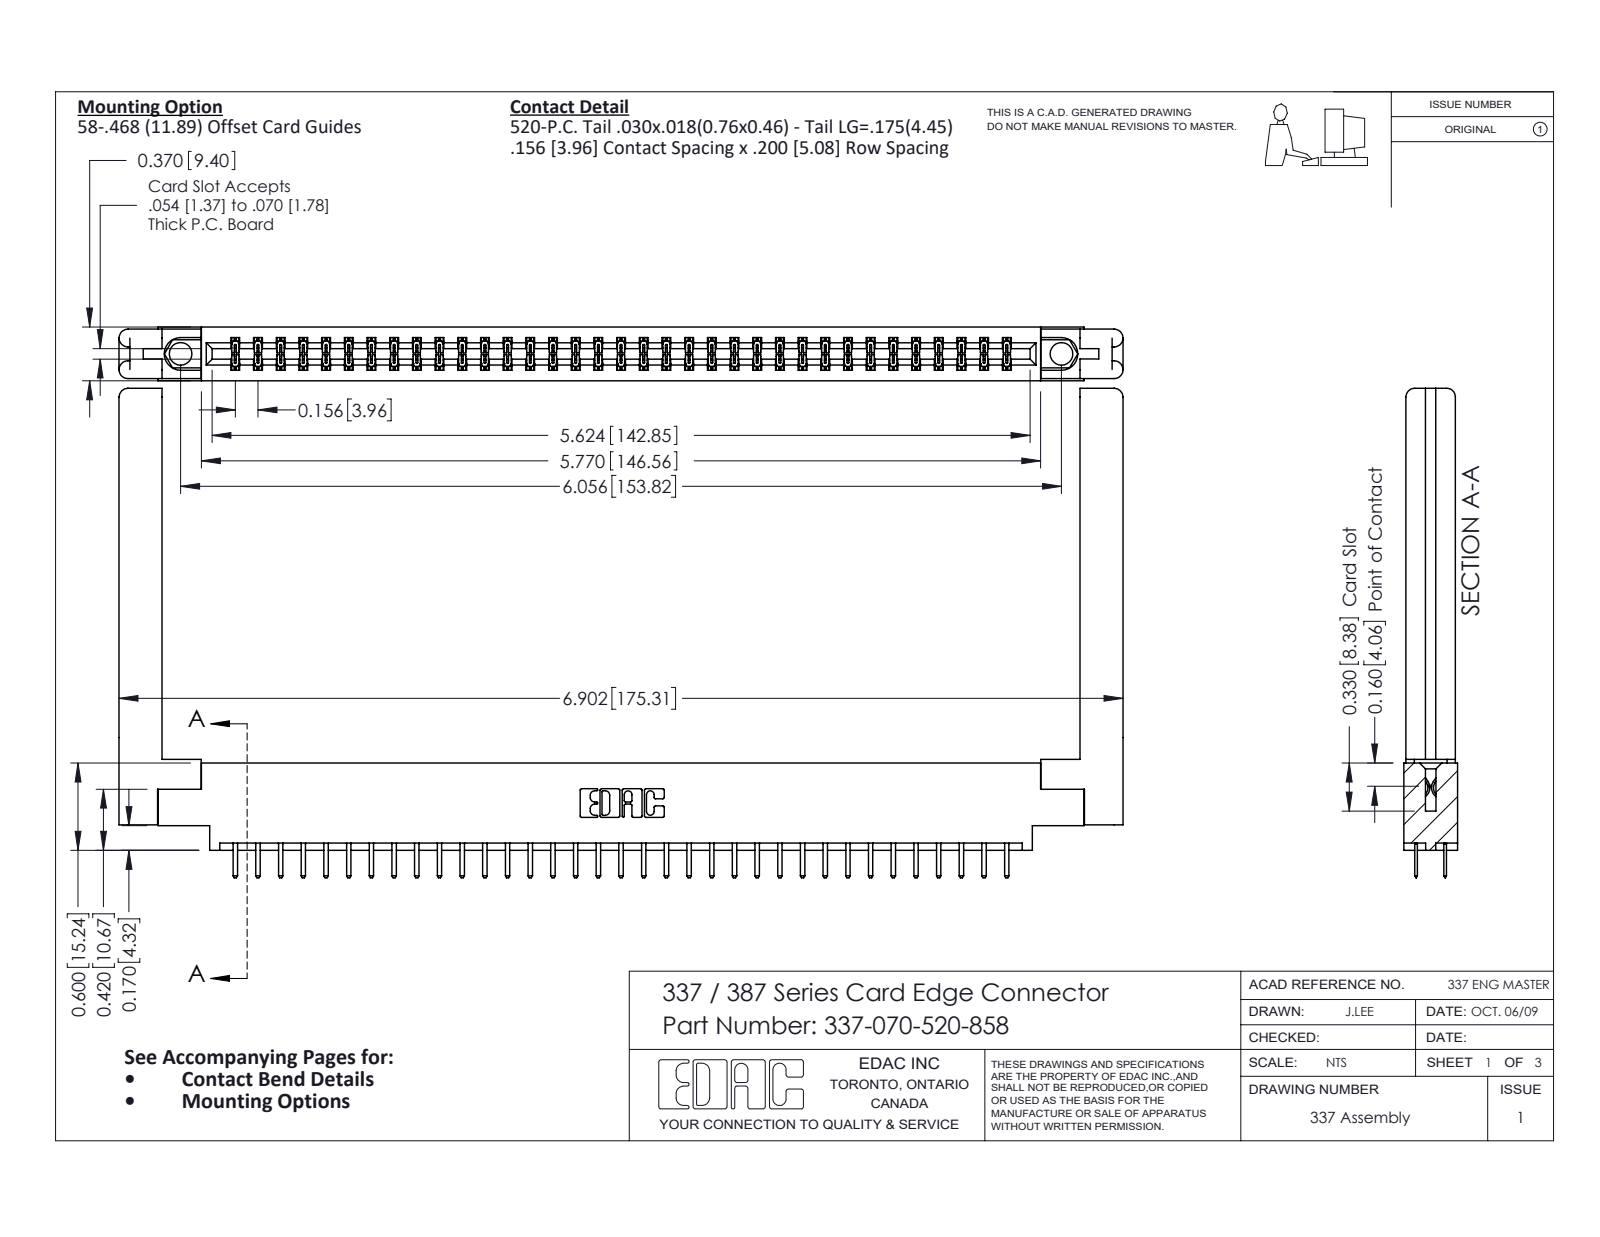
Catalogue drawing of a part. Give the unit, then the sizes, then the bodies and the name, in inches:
Units: inches
Overall size (bounding box): 6.902 × 3.363 × 0.37
Round holes (diameter × count): ⌀0.089 ×2, ⌀0.125 ×2, ⌀0.156 ×2
Round bosses / shafts (diameter × count): ⌀0.155 ×2
Partial cylindrical surfaces — rounded edges, fillets, slot ends (radius × count): R0.006 ×106, R0.01 ×74, R0.01 ×22, R0.061 ×8, R0.007 ×6, R0.031 ×6, R0.06 ×5, R0.026 ×3
Main face-to-face distances: 0.37, 0.298, 0.072, 0.355, 0.015, 0.057, 0.283, 0.2, 0.149, 0.135
Hole centre spacings: 6.056
Volume: 1.549 in³ · Surface area: 39.7 in²
Bodies: 75 solids, 4320 faces (2958 planar, 1338 cylindrical, 24 other)
Part name (STEP PRODUCT): 337-070-520-858; 345-292-001_345-293-120; 307-220-058; 337 Part_0.170 Offset - 0.156 Dia-TI (+1 more)
STEP written by: SolidWorks 2016 (CONFIG_CONTROL_DESIGN)
